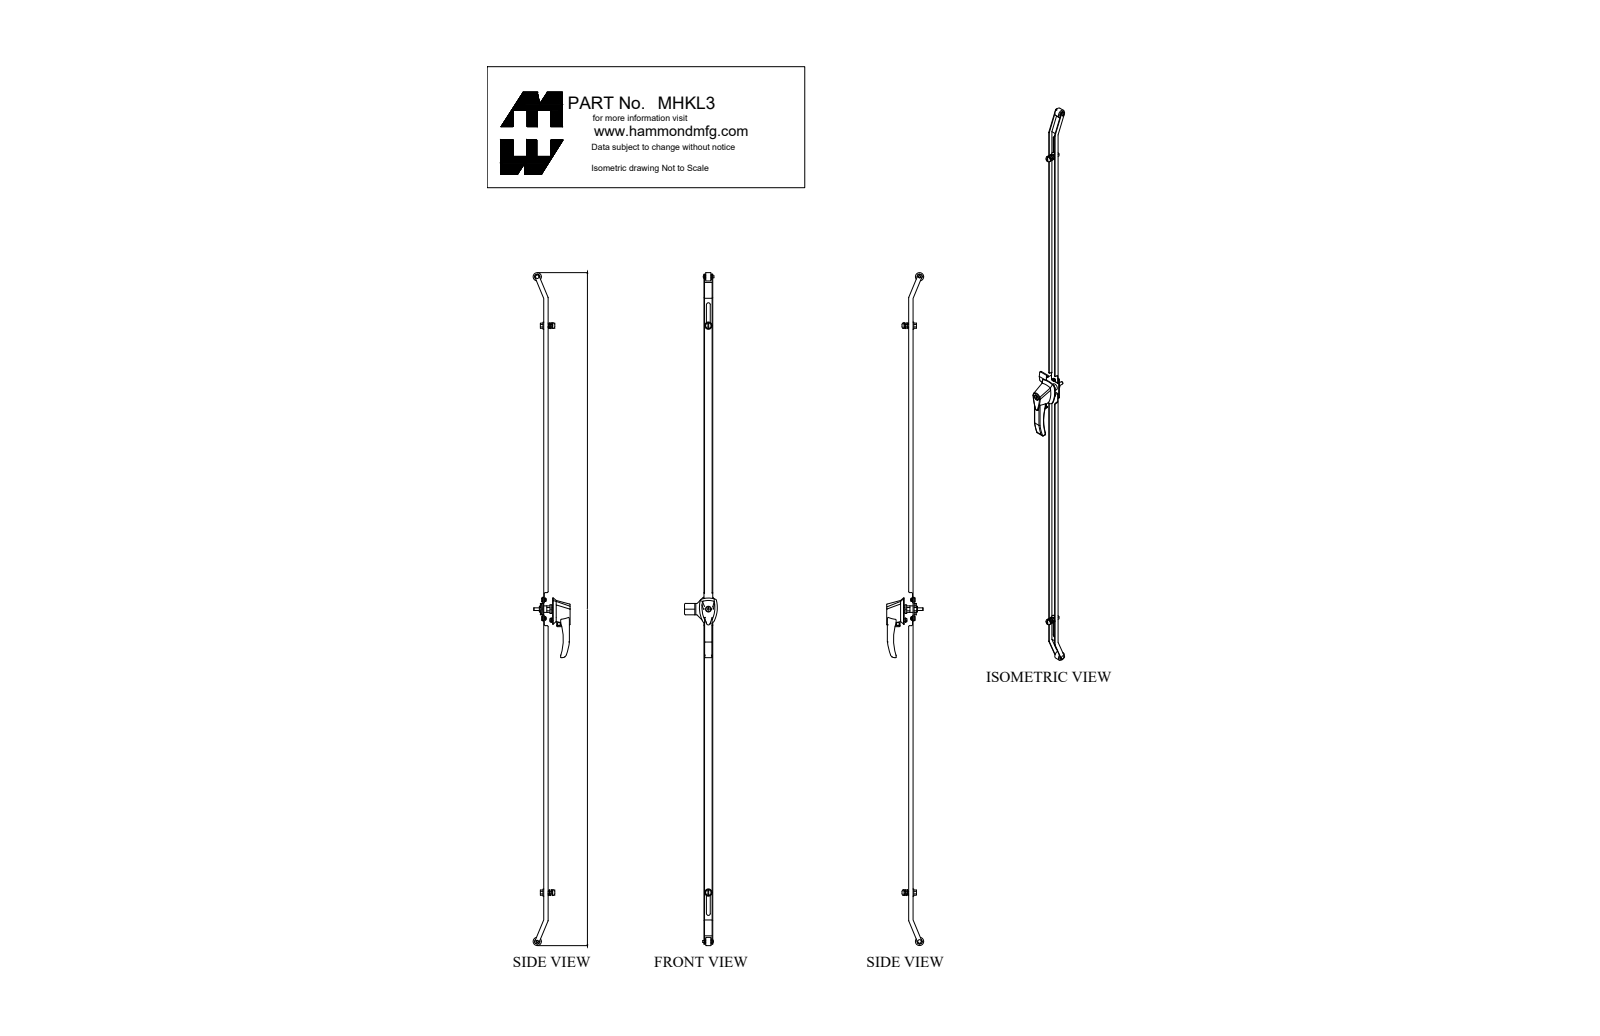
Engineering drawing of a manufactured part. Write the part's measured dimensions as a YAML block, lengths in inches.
part_name: "MHKL3"
step_written_by: "SolidWorks 2018 (AUTOMOTIVE_DESIGN)"
units: inches
bodies: {solids: 32, faces: 552, planar: 275, cylindrical: 214, other: 63}
overall_size: [81.493, 4.473, 3.975]
volume: 24.4
surface_area: 416.6
round_holes:
  - {diameter: 0.375, count: 3}
  - {diameter: 0.159, count: 2}
  - {diameter: 0.195, count: 2}
  - {diameter: 0.25, count: 2}
  - {diameter: 0.257, count: 2}
  - {diameter: 0.28, count: 2}
  - {diameter: 0.281, count: 2}
  - {diameter: 0.307, count: 2}
  - {diameter: 0.39, count: 2}
  - {diameter: 0.413, count: 2}
  - {diameter: 0.173, count: 1}
  - {diameter: 0.233, count: 1}
round_bosses_or_shafts:
  - {diameter: 0.325, count: 3}
  - {diameter: 1, count: 2}
  - {diameter: 0.882, count: 2}
  - {diameter: 0.678, count: 2}
  - {diameter: 0.63, count: 2}
  - {diameter: 0.402, count: 2}
  - {diameter: 0.375, count: 2}
  - {diameter: 0.278, count: 2}
partial_cylinders:
  - {radius: 0.125, count: 22}
  - {radius: 0.03, count: 6}
  - {radius: 0.06, count: 6}
  - {radius: 0.09, count: 6}
  - {radius: 0.01, count: 4}
  - {radius: 0.234, count: 4}
  - {radius: 0.312, count: 2}
  - {radius: 0.75, count: 2}
face_to_face_distances: [0.07, 0.992, 1.062, 0.922, 0.531, 0.461, 0.076, 0.986, 0.916, 0.125]
hole_center_spacings: [1.126, 1.287, 33.202, 34.327, 34.333, 35.453, 0.213, 0.625]
